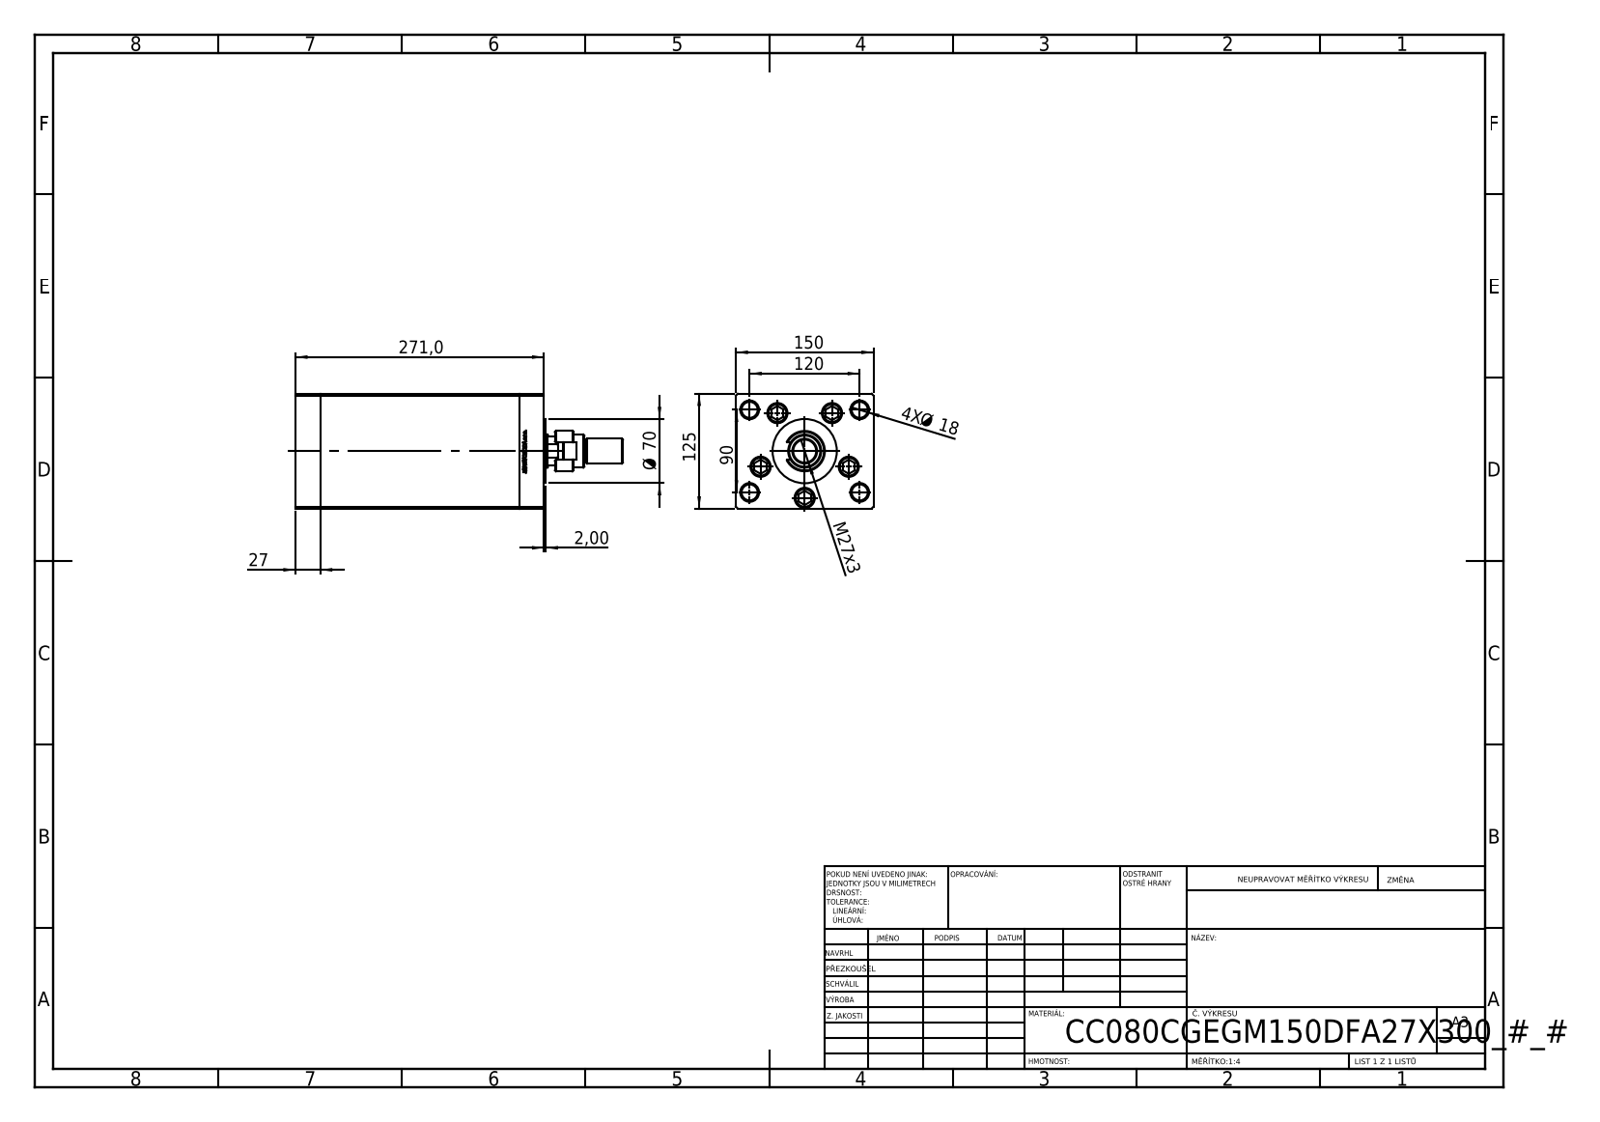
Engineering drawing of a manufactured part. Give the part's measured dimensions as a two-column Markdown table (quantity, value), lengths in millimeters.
| quantity | value |
| --- | --- |
| part name | V220C FRONT; V220C BACK_C; V220C_C MIDDLE; V220C_VC_C (+2 more) |
| STEP written by | SolidWorks 2019 (CONFIG_CONTROL_DESIGN) |
| units | millimeters |
| bodies | 14 solids, 1196 faces (554 planar, 168 cylindrical, 474 other) |
| overall size | 356.8 × 150 × 125 |
| volume | 4 177 000 mm³ |
| surface area | 462 188 mm² |
| round holes (diameter × count) | 17.5 × 9, 22 × 5, 16 × 4, 20.5 × 4, 21 × 1, 25.5 × 1 |
| round bosses / shafts (diameter × count) | 8 × 5, 21 × 4, 80 × 1, 70 × 1, 44 × 1, 36 × 1, 27 × 1, 25 × 1 |
| partial cylindrical surfaces (radius × count) | 0.93 × 2, 9.5 × 1, 15 × 1, 17.5 × 1 |
| main face-to-face distances | 150, 125, 27, 244, 217, 33.5, 6.5, 271, 237.5, 210.5 |
| hole center spacings | 51, 75, 30.43, 30.48, 58.89, 60.3, 61.25, 63.14 |
